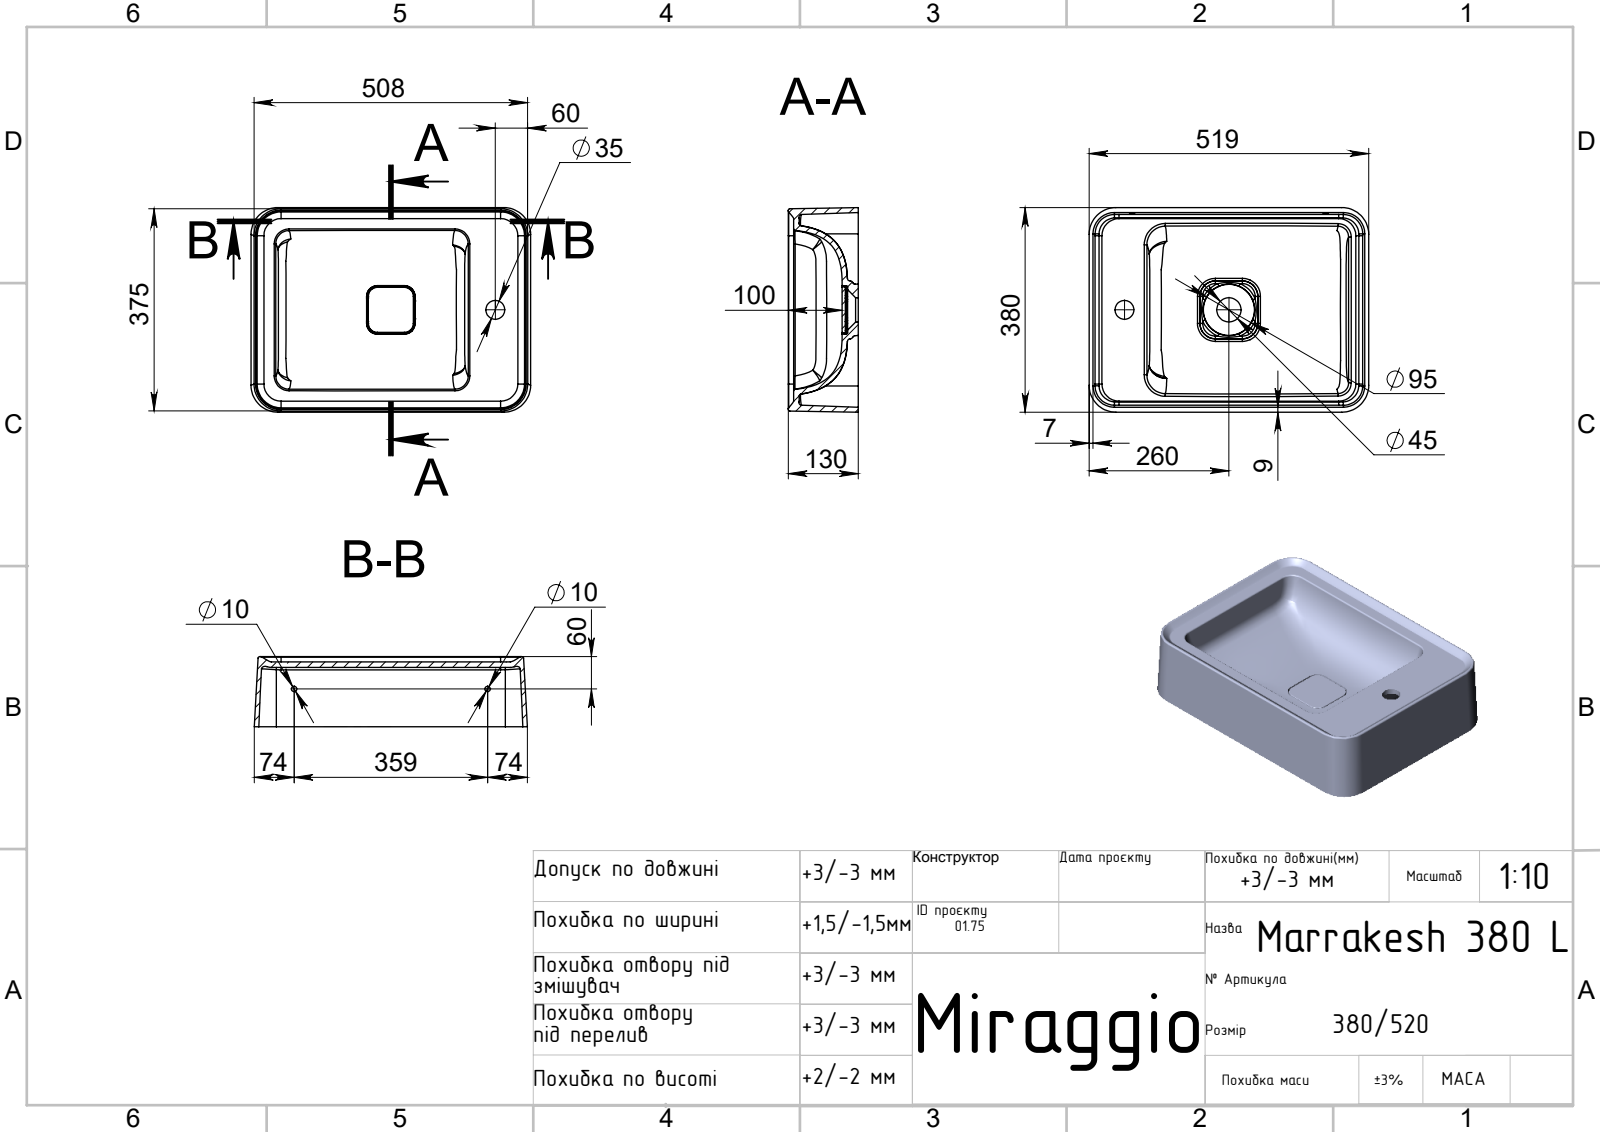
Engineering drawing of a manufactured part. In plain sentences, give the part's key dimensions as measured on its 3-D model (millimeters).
The part is named "Marrakesh 380 L". Its 3-D file was written by "SolidWorks 2020 (AUTOMOTIVE_DESIGN)". It is 2 solids with 254 faces: 40 planar, 44 cylindrical and 170 other. Overall it measures 519.12 by 379.65 by 130 millimeters. Its volume is 4 306 000 cubic millimeters and its surface area 923 978 square millimeters. Round holes: 2 of diameter 10, 1 of diameter 35, 1 of diameter 45. Partial cylindrical surfaces (rounded edges, fillets, slot ends): 7 of radius 3, 7 of radius 5, 5 of radius 1.8, 5 of radius 2, 4 of radius 1, 4 of radius 50, 1 of radius 45. The main face-to-face distances are 10, 110, 120, 90, 24, 86, 96, 30, 6, 80. The hole center spacings are 193.88, 359.12.
